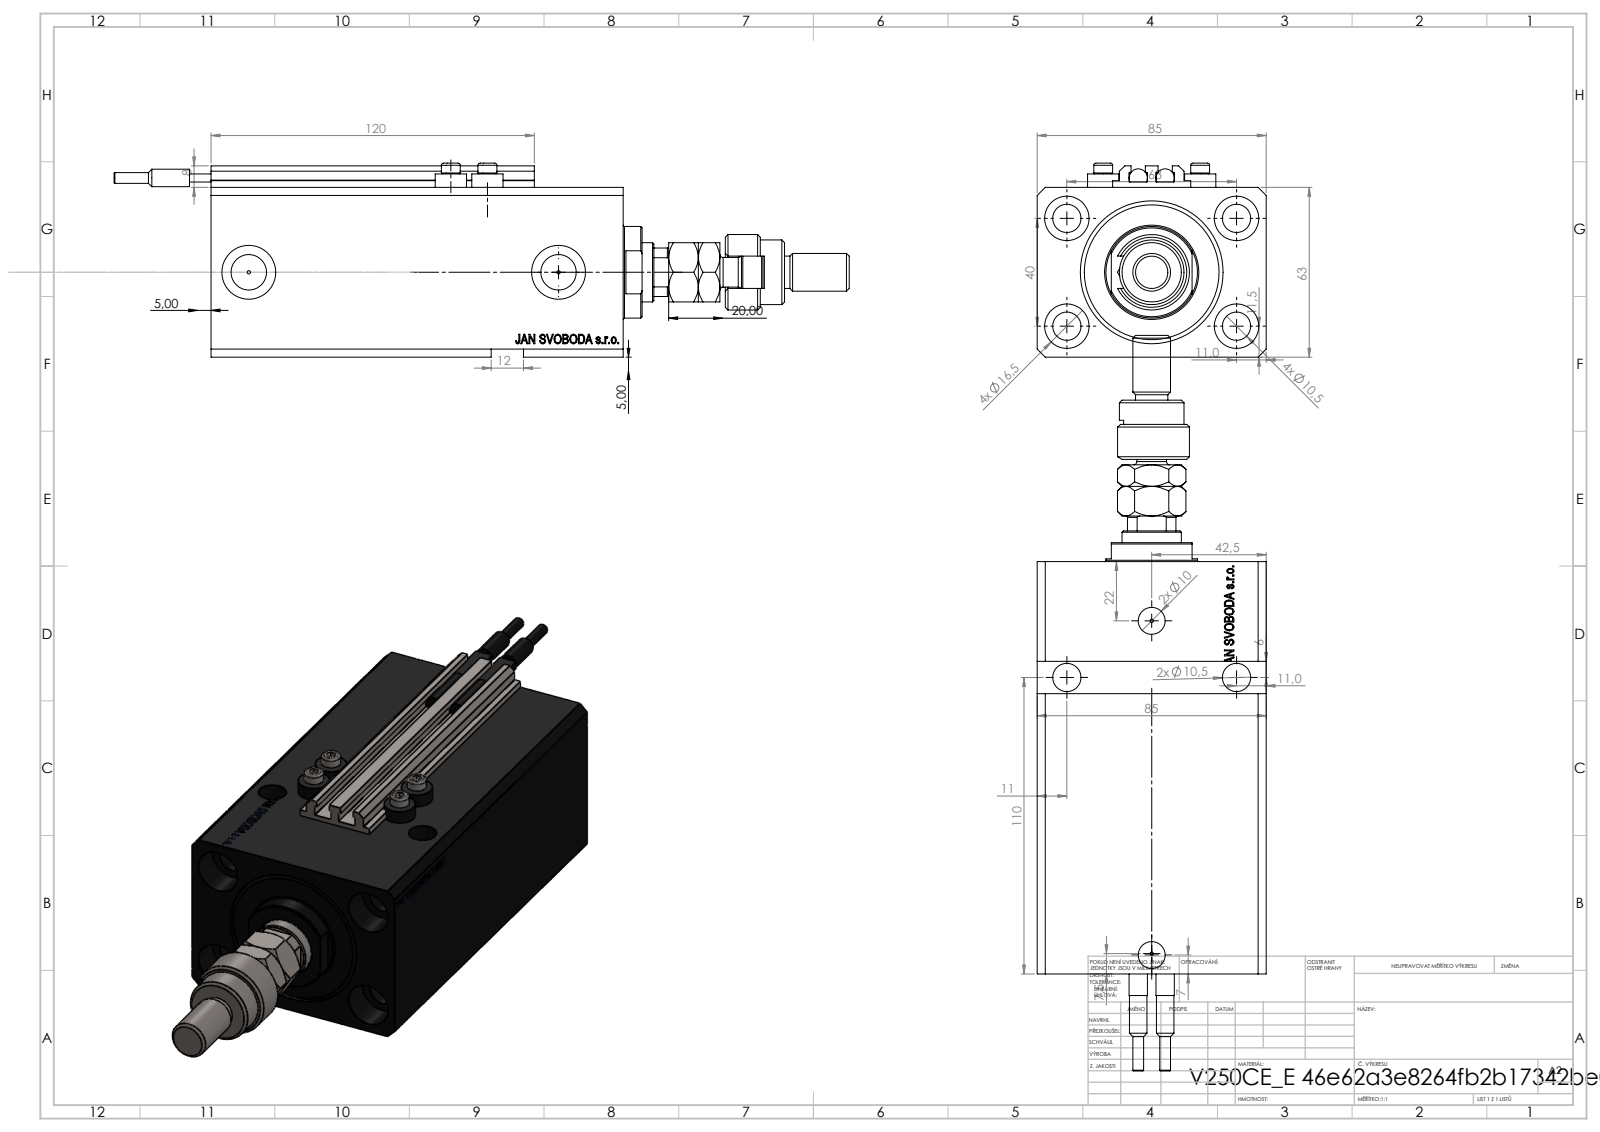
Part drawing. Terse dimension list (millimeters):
name: SWITCH_V250CE; V250CE_C_VCP; MFA; ALLEN BOLT V250CE (+3 more)
written by: SolidWorks 2019 (CONFIG_CONTROL_DESIGN)
unit: mm
bodies: 12 solids, 1244 faces (595 planar, 171 cylindrical, 478 other)
size: 273 × 85 × 72
volume: 709 336 mm³; area: 151 534 mm²
holes: 8× ⌀10.5, 4× ⌀1.25, 4× ⌀4, 4× ⌀16.5, 2× ⌀10, 2× ⌀13.16, 2× ⌀20, 1× ⌀12.5, 1× ⌀22, 1× ⌀40, 1× ⌀53
bosses: 4× ⌀11.6, 4× ⌀7, 2× ⌀6.8, 2× ⌀6.5, 2× ⌀4, 1× ⌀34, 1× ⌀28, 1× ⌀24
rounds: 10× R0.2, 1× R9.75, 1× R10.5
face distances: 63, 85, 17, 153, 136, 3, 65, 11.4, 124.6, 141.6
hole spacings: 37.31, 63, 13.6, 15.4, 24.96, 33.62, 36, 37.86
